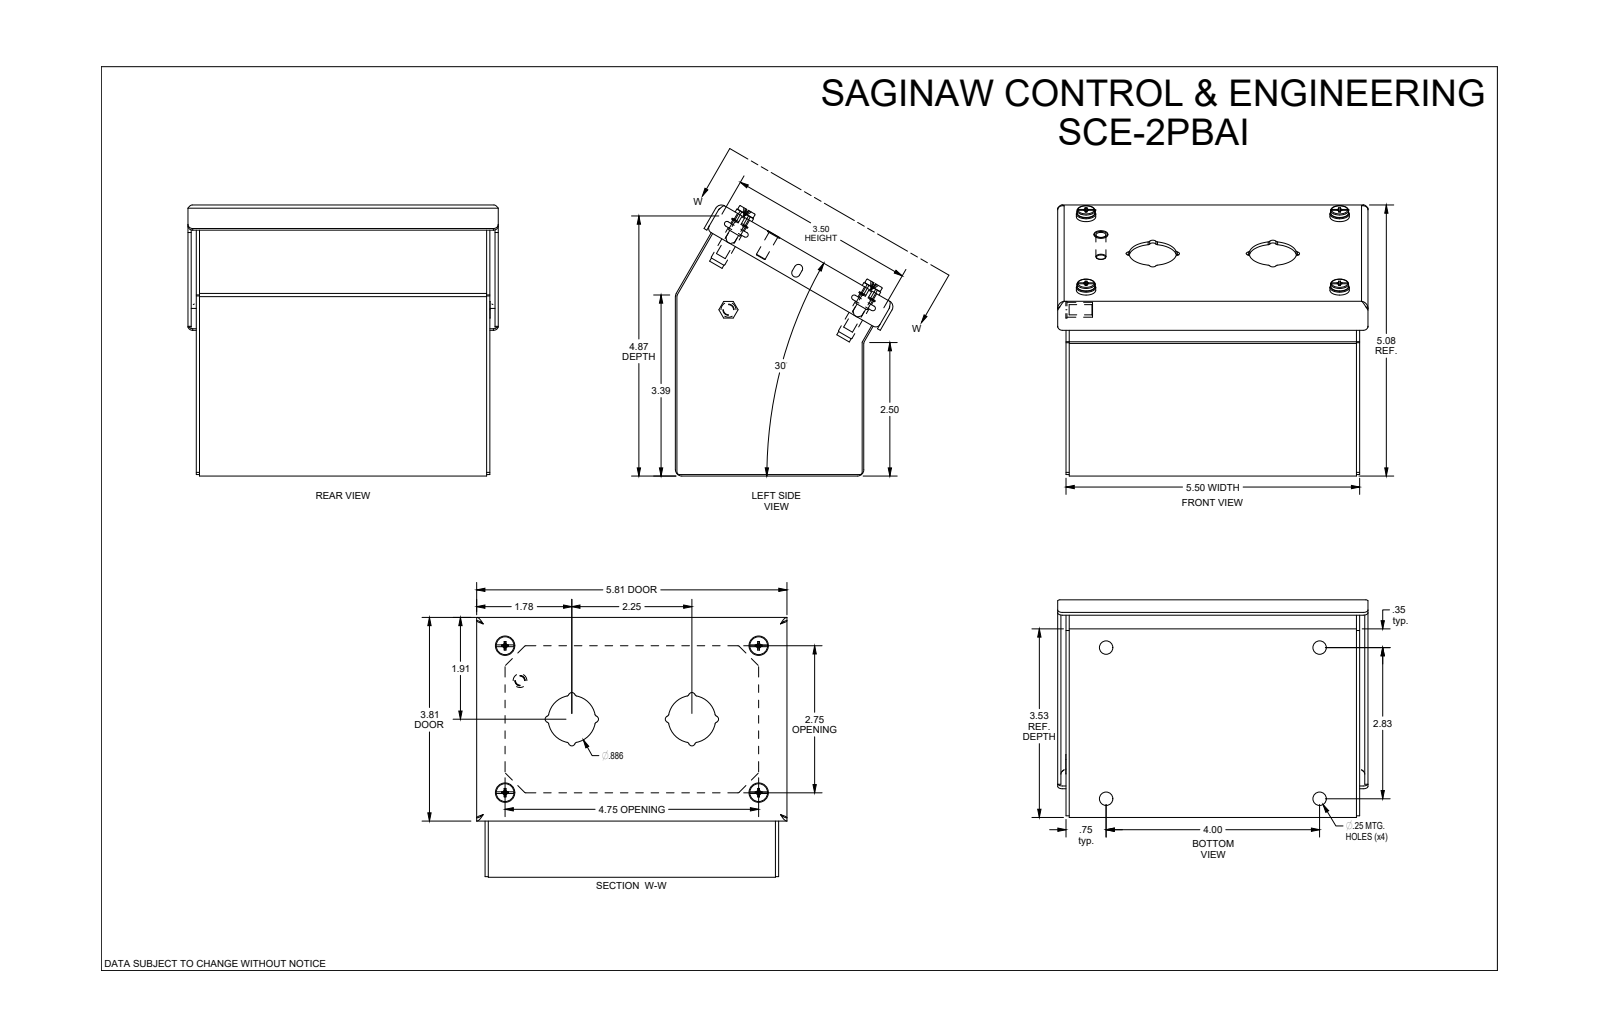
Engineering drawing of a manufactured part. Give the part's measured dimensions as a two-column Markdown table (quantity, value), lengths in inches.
| quantity | value |
| --- | --- |
| part name | SCE-2PBAI |
| STEP written by | SolidWorks 2021 (AUTOMOTIVE_DESIGN) |
| units | inches |
| bodies | 19 solids, 628 faces (240 planar, 216 cylindrical, 172 other) |
| overall size | 5.812 × 5.098 × 4.097 |
| volume | 8.238 in³ |
| surface area | 280.2 in² |
| round holes (diameter × count) | 0.25 × 8, 0.19 × 5, 0.22 × 4, 0.266 × 4, 0.317 × 4 |
| round bosses / shafts (diameter × count) | 0.188 × 5, 0.362 × 4, 0.34 × 4, 0.334 × 4, 0.292 × 4, 0.27 × 4, 0.26 × 4, 0.146 × 4 |
| partial cylindrical surfaces (radius × count) | 0.04 × 20, 0.06 × 20, 0.03 × 12, 0.01 × 10, 0.062 × 8, 0.115 × 8, 0.24 × 8, 0.12 × 6 |
| main face-to-face distances | 0.06, 5.44, 0.06, 5.38, 5.5, 3.47, 0.156, 3.47, 3.41, 3.53 |
| hole center spacings | 4.75, 2.75, 2.753, 2.83, 4, 4.9, 5.489, 5.49 |
